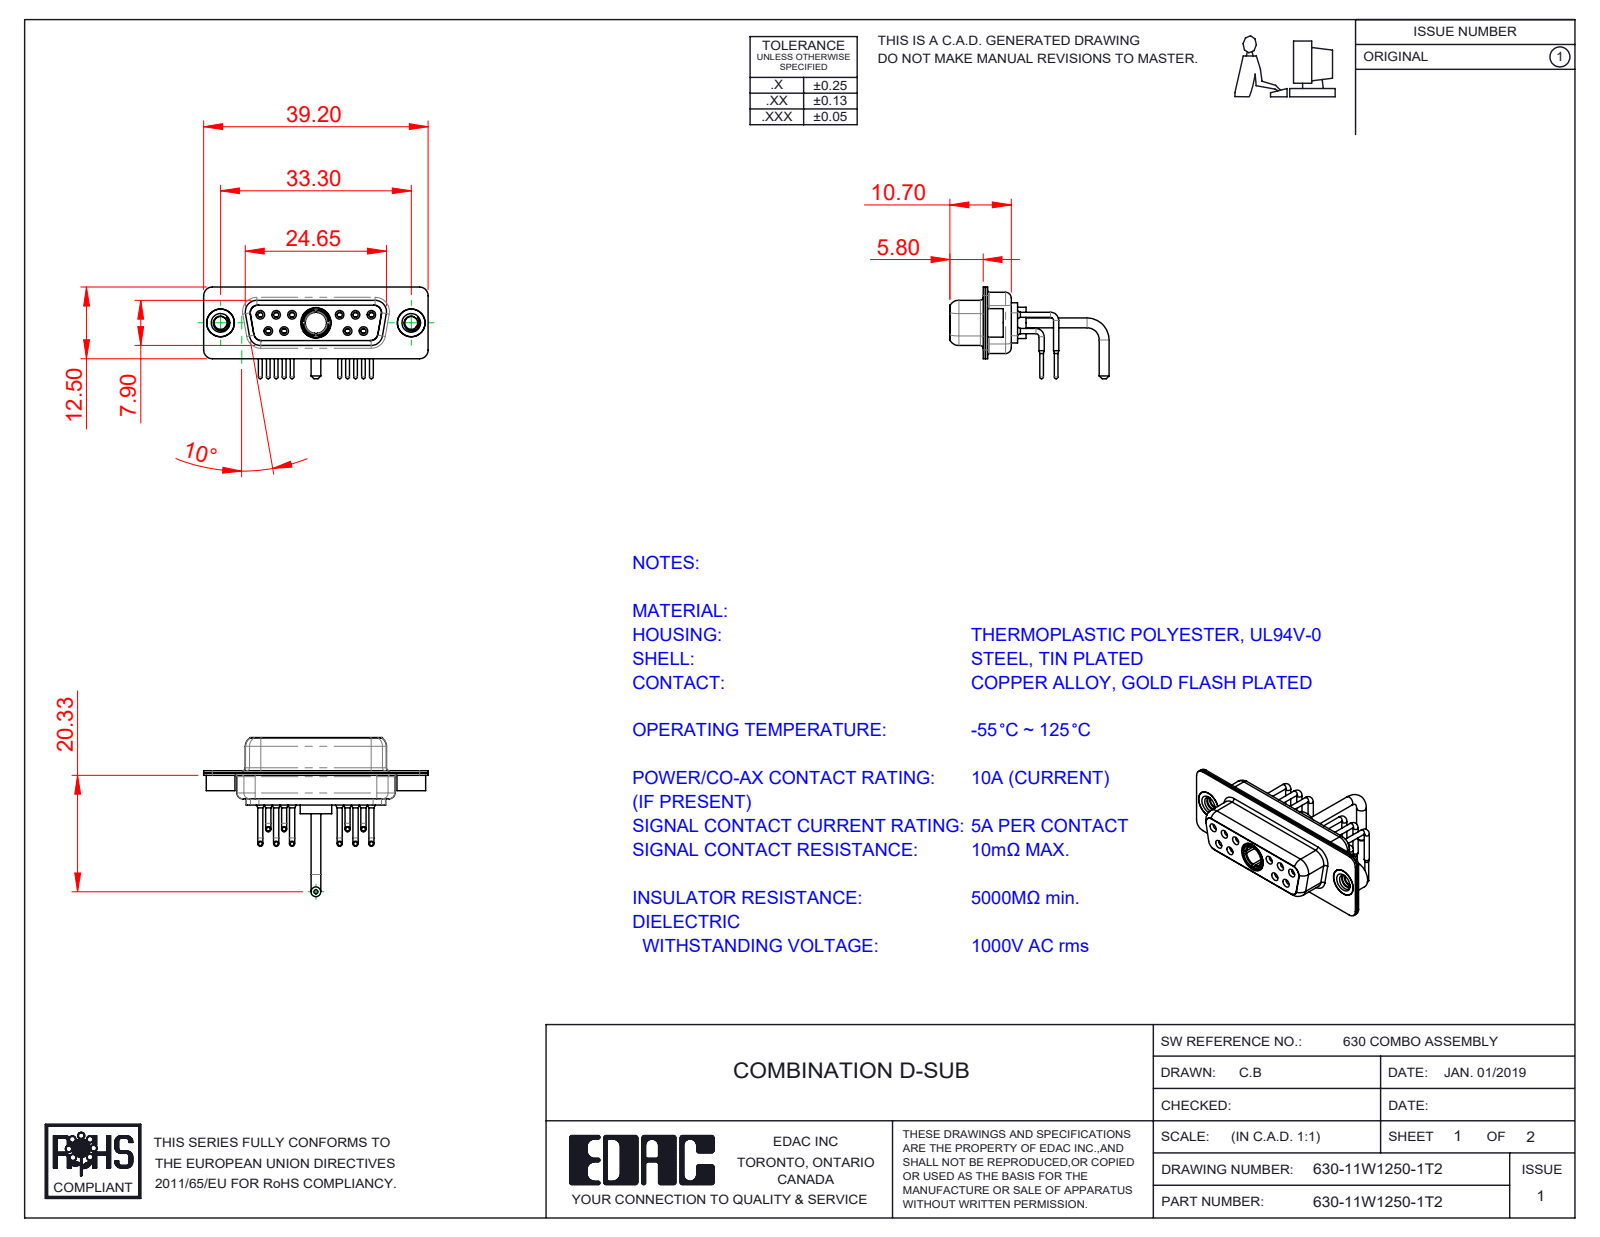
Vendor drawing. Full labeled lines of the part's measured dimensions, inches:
Part name (STEP PRODUCT): 630Combo Contact Row 2; 630Combo Contact Row 1; 630-11W1250-1T2; 630Combo Shell Rear_15 Contacts (+4 more)
STEP written by: SolidWorks 2020 (CONFIG_CONTROL_DESIGN)
Units: inches
Bodies: 17 solids, 887 faces (246 planar, 392 cylindrical, 249 other)
Overall size (bounding box): 1.543 × 1.094 × 0.63
Volume: 0.159 in³ · Surface area: 9.701 in²
Round holes (diameter × count): ⌀0.035 ×10, ⌀0.043 ×10, ⌀0.059 ×10, ⌀0.079 ×10, ⌀0.067 ×6, ⌀0.063 ×4, ⌀0.191 ×3, ⌀0.089 ×2, ⌀0.157 ×2, ⌀0.159 ×2, ⌀0.146 ×1, ⌀0.209 ×1
Round bosses / shafts (diameter × count): ⌀0.035 ×10, ⌀0.026 ×10, ⌀0.063 ×6, ⌀0.197 ×2, ⌀0.195 ×2, ⌀0.189 ×2, ⌀0.067 ×2, ⌀0.217 ×1
Partial cylindrical surfaces — rounded edges, fillets, slot ends (radius × count): R0.059 ×16, R0.053 ×12, R0.079 ×12, R0.063 ×8, R0.01 ×4, R0.02 ×4, R0.024 ×4, R0.026 ×4
Main face-to-face distances: 0.016, 0.055, 0.018, 0.333, 0.071, 0.35, 0.031, 0.244, 0.278, 0.073
Hole centre spacings: 0.124, 0.109, 0.545, 0.436, 0.654, 0.198, 0.198, 0.218
